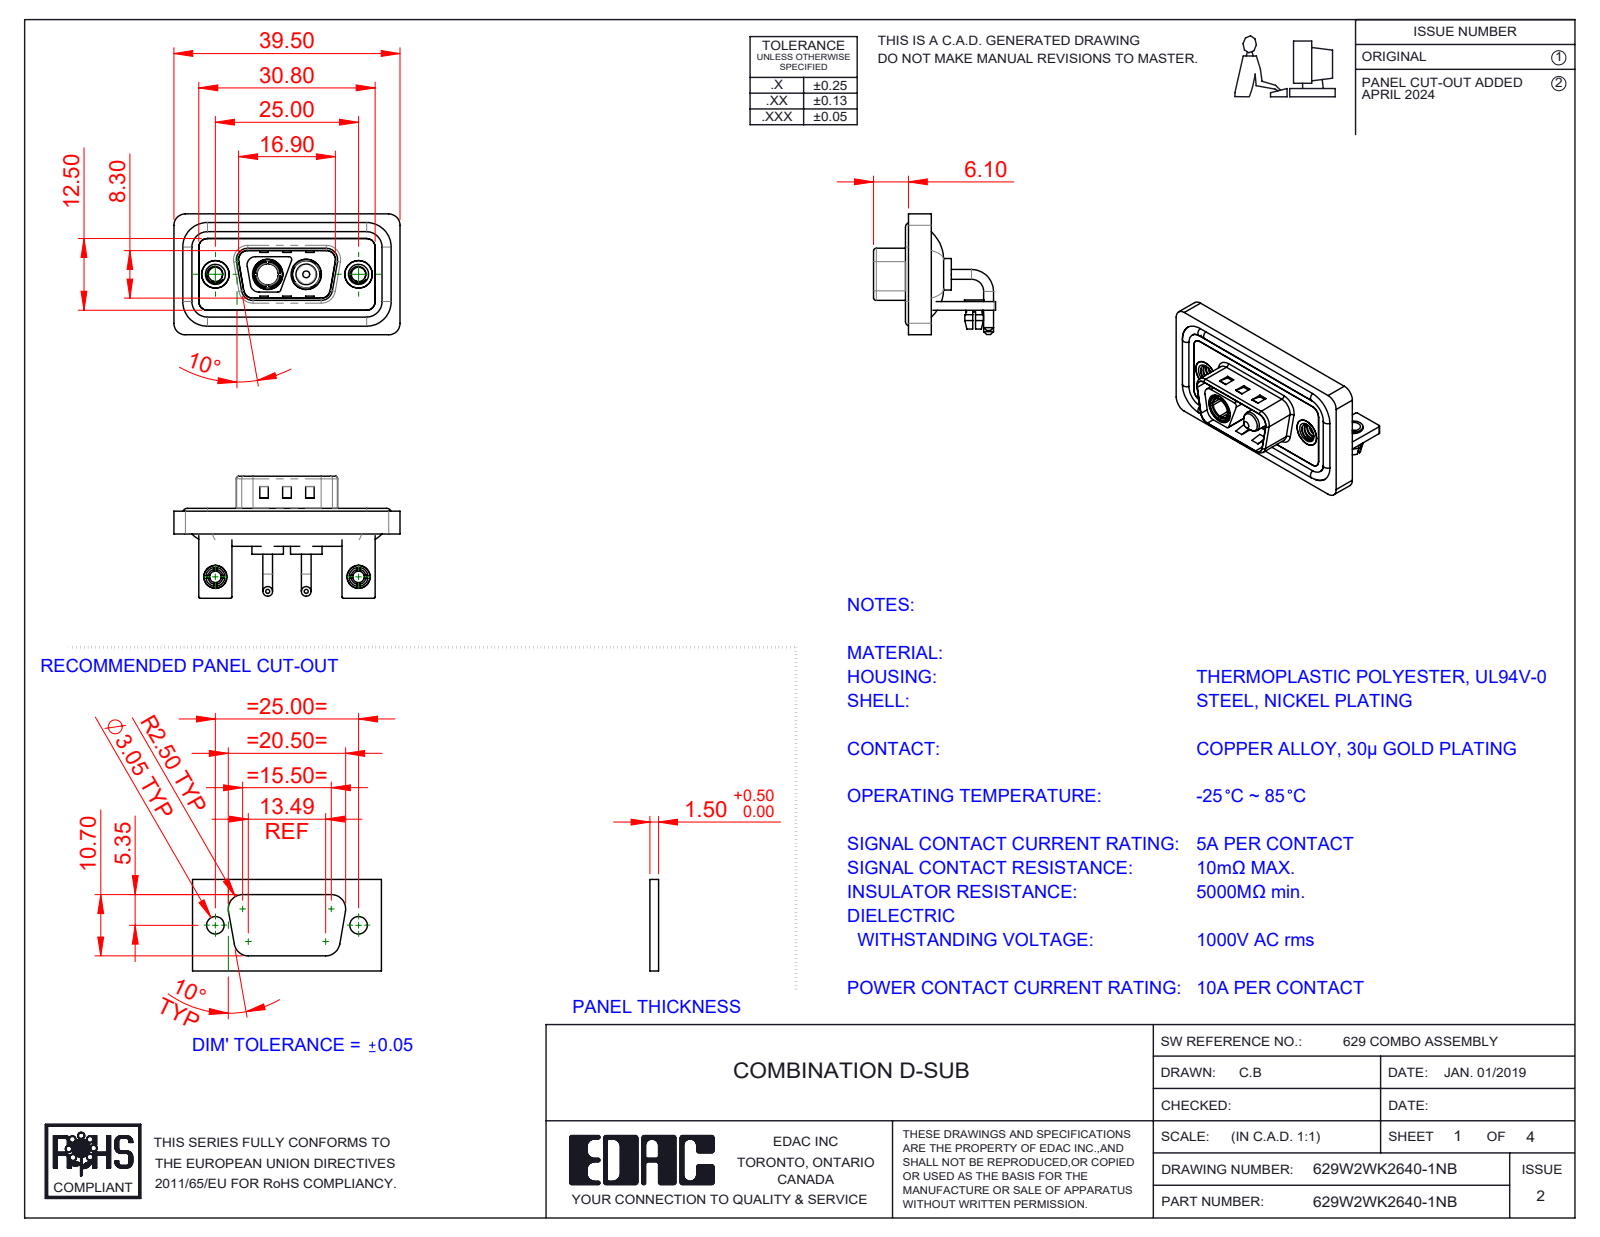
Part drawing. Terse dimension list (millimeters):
name: 629Combo Shell Front_09 Contacts; 629Combo Threaded Rivet_B; 629Combo Housing_2WK2; 629Combo Shell Rear_09 Contacts (+6 more)
written by: SolidWorks 2023 (CONFIG_CONTROL_DESIGN)
unit: mm
bodies: 15 solids, 672 faces (257 planar, 281 cylindrical, 134 other)
size: 39.5 × 21.3 × 21.1
volume: 4 872 mm³; area: 8 226 mm²
holes: 4× ⌀2.5, 2× ⌀2, 2× ⌀3.2, 2× ⌀4, 2× ⌀4.8, 2× ⌀4.85, 2× ⌀5, 2× ⌀5.3, 1× ⌀3.7
bosses: 4× ⌀1.7, 4× ⌀1.6, 2× ⌀5.5, 2× ⌀5.2, 2× ⌀4.9, 2× ⌀4.75, 2× ⌀4, 2× ⌀3.75
rounds: 20× R1.5, 19× R2, 16× R0.25, 11× R0.5, 8× R1.6, 4× R0.6, 4× R0.65, 4× R0.9
face distances: 0.4, 1.5, 2.9, 0.8, 1.1, 1.2, 2.1, 1.6, 3.7, 2.5
hole spacings: 9.14, 15.86, 25, 6.72
